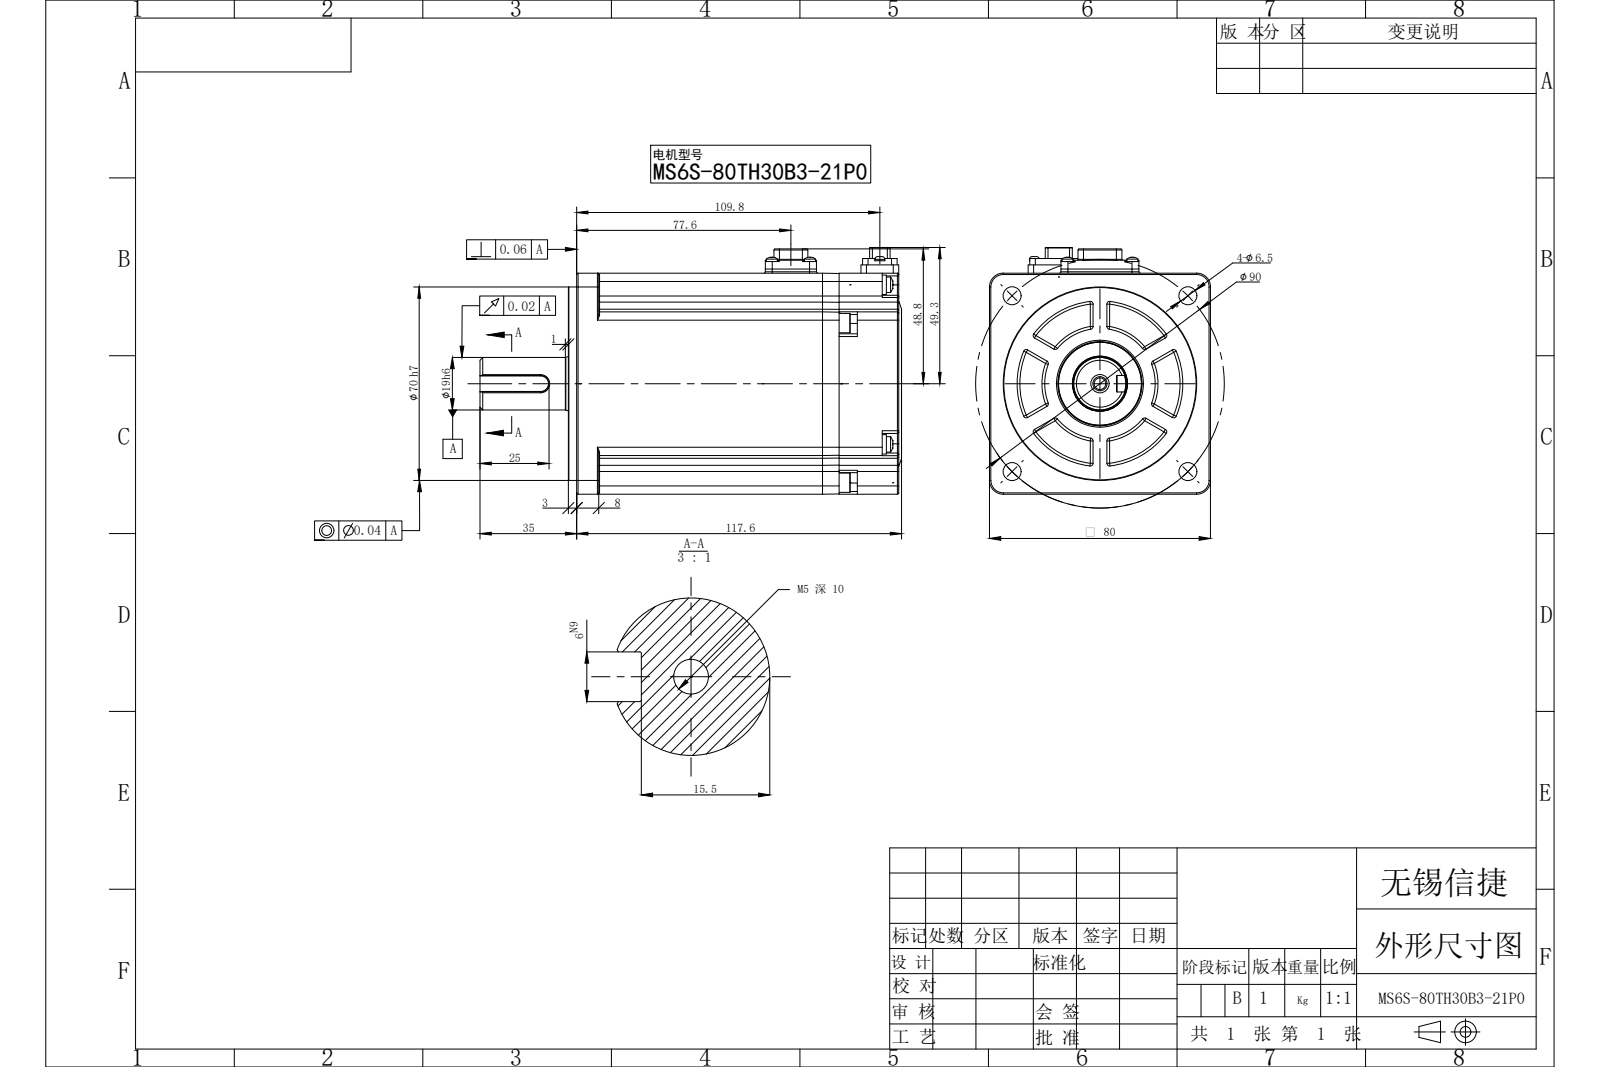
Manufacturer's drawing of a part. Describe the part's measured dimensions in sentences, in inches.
The part is named "MS6S-80TH30B3-21P0". Its 3-D file was written by "SolidWorks 2022 (CONFIG_CONTROL_DESIGN)". It is 0 solids with 882 faces: 380 planar, 298 cylindrical and 204 other. Overall it measures 6.008 by 3.516 by 3.15 inches. Round holes: 4 of diameter 0.083, 4 of diameter 0.256, 2 of diameter 0.063, 1 of diameter 0.165, 1 of diameter 0.787. Round bosses or shafts: 8 of diameter 0.276, 4 of diameter 0.22, 4 of diameter 0.157, 2 of diameter 0.138, 1 of diameter 2.756, 1 of diameter 1.181, 1 of diameter 0.78, 1 of diameter 0.748. Partial cylindrical surfaces (rounded edges, fillets, slot ends): 50 of radius 0.039, 40 of radius 0.02, 17 of radius 0.118, 16 of radius 0.008, 14 of radius 0.012, 12 of radius 0.079, 8 of radius 0.148, 4 of radius 0.024. The main face-to-face distances are 3.15, 0.551, 2.598, 4.591, 0.039, 4.63, 2.047, 0.118, 1.087, 1.126. The hole center spacings are 1.772, 2.506, 0.315, 0.654, 0.726, 3.543, 0.925, 1.129.
